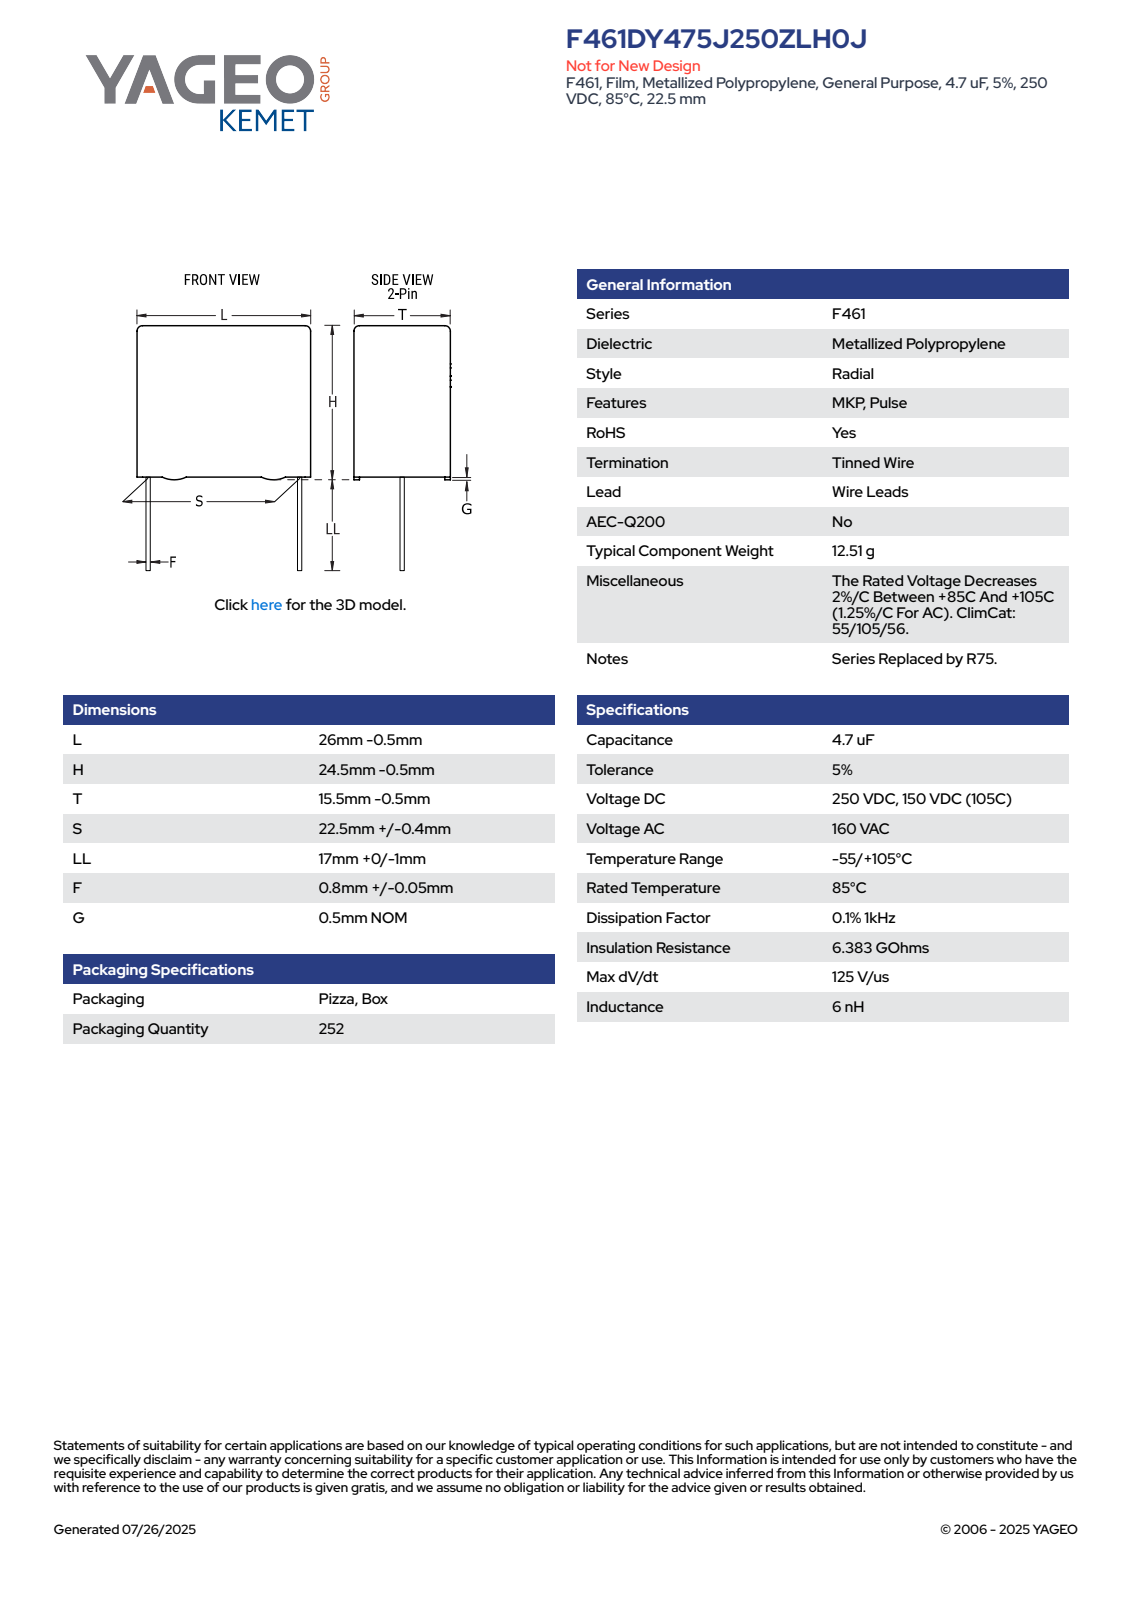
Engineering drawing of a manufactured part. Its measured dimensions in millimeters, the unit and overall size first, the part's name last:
Units: millimetres
Overall size (bounding box): 41 × 25.5 × 15.01
Round bosses / shafts (diameter × count): ⌀0.85 ×2
Partial cylindrical surfaces — rounded edges, fillets, slot ends (radius × count): R0.5 ×4
Main face-to-face distances: 15, 25.5, 23.5, 0.5, 24, 0.85, 14.14, 0.86, 13.29, 14.15
Volume: 9 011 mm³ · Surface area: 2 833 mm²
Bodies: 4 solids, 89 faces (81 planar, 8 cylindrical, 0 other)
Part name (STEP PRODUCT): CFR_RBG_26X24.5X15.5_L25.5H24T15S22.5LL17F0.85G0.5
STEP written by: SolidWorks 2014 (AUTOMOTIVE_DESIGN)
